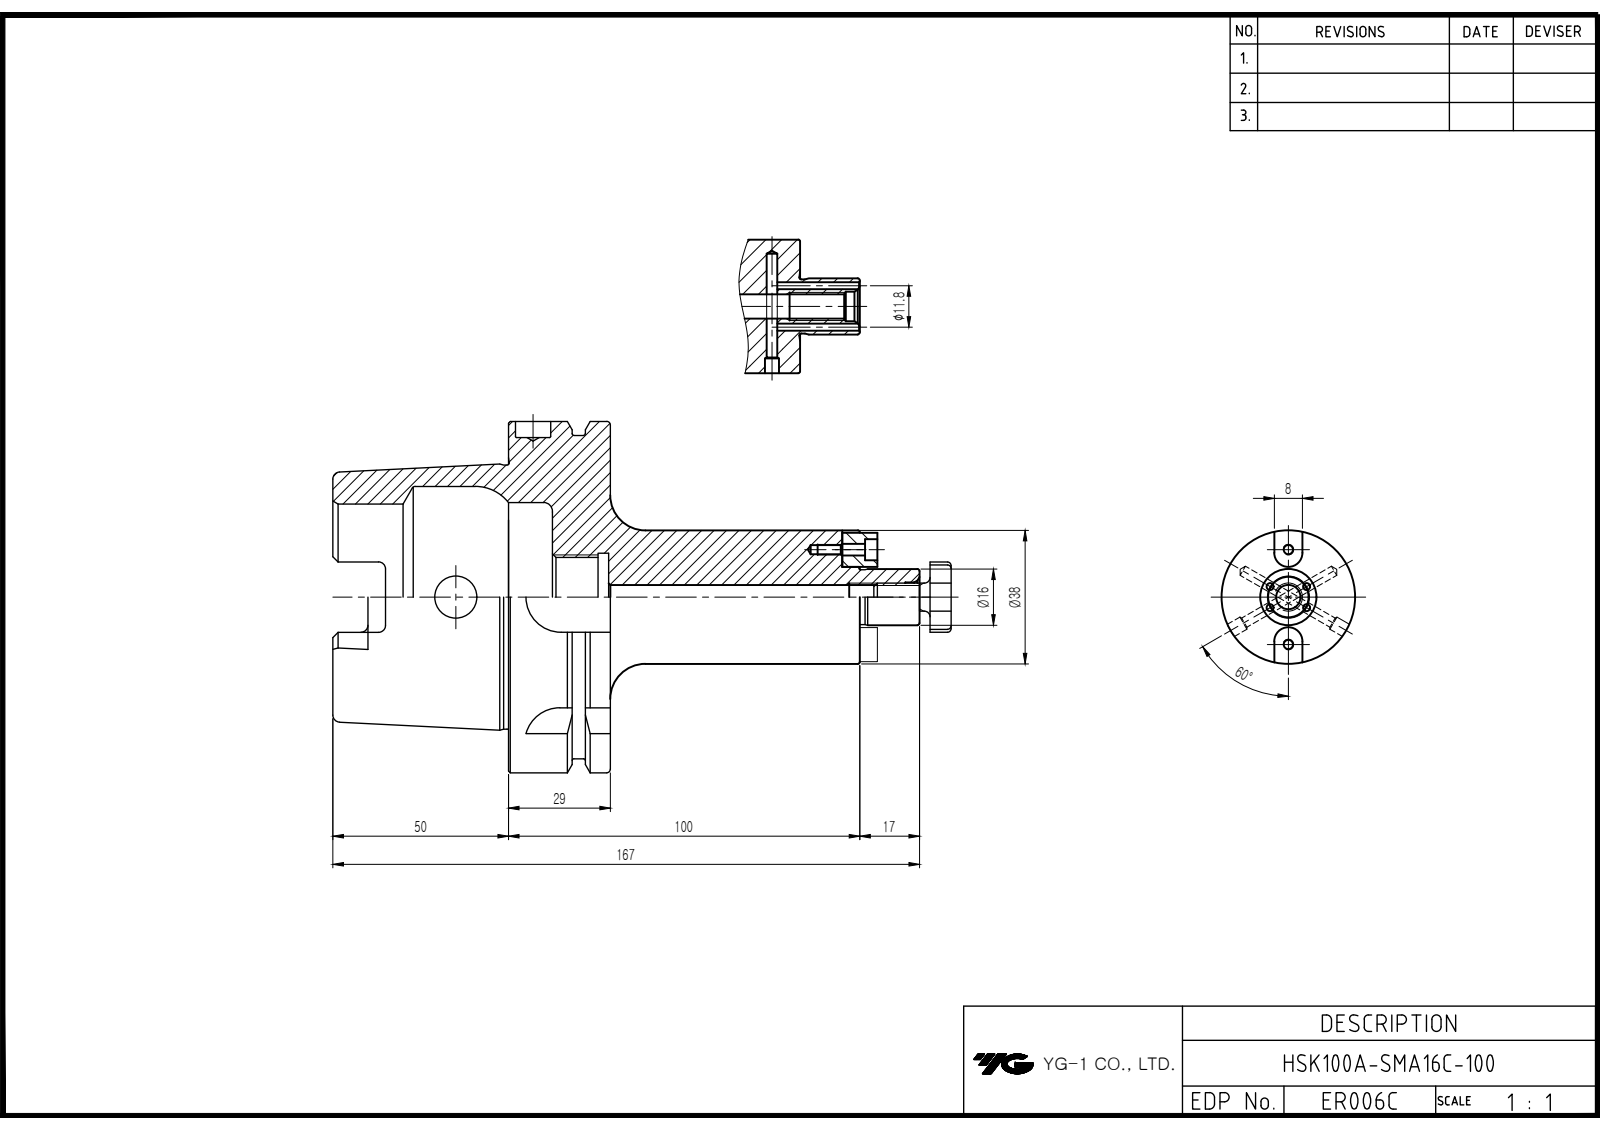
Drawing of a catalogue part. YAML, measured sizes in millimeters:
part_name: "LO-HSK100A-SMA16C-100; SMA16E-DRIVE KEY-SECO; HEX'' WRENCH BOLT-M3x0.5x12L; SMA16-M8x1.25x16L"
step_written_by: "Autodesk Inventor 2025 (AP242_MANAGED_MODEL_BASED_3D_ENGINEERING_MIM_LF)"
units: millimeters
bodies: {solids: 6, faces: 205, planar: 85, cylindrical: 61, other: 59}
overall_size: [178, 100, 100]
volume: 340385
surface_area: 64172
round_holes:
  - {diameter: 2, count: 4}
  - {diameter: 2.46, count: 2}
  - {diameter: 3.3, count: 2}
  - {diameter: 6, count: 2}
  - {diameter: 6.65, count: 1}
  - {diameter: 8.4, count: 1}
  - {diameter: 10, count: 1}
  - {diameter: 12, count: 1}
  - {diameter: 22.38, count: 1}
  - {diameter: 25, count: 1}
  - {diameter: 53, count: 1}
  - {diameter: 63, count: 1}
round_bosses_or_shafts:
  - {diameter: 5.5, count: 2}
  - {diameter: 3, count: 2}
  - {diameter: 100, count: 1}
  - {diameter: 92, count: 1}
  - {diameter: 75.41, count: 1}
  - {diameter: 38, count: 1}
  - {diameter: 16, count: 1}
  - {diameter: 8, count: 1}
partial_cylinders:
  - {radius: 2, count: 10}
  - {radius: 10, count: 5}
  - {radius: 4, count: 4}
  - {radius: 4.88, count: 4}
face_to_face_distances: [29, 12.5, 16.5, 62.5, 79, 50, 150, 100, 87.5, 71]
hole_center_spacings: [5.9, 11.72, 17.23, 10.22, 11.8, 13.5, 27]
